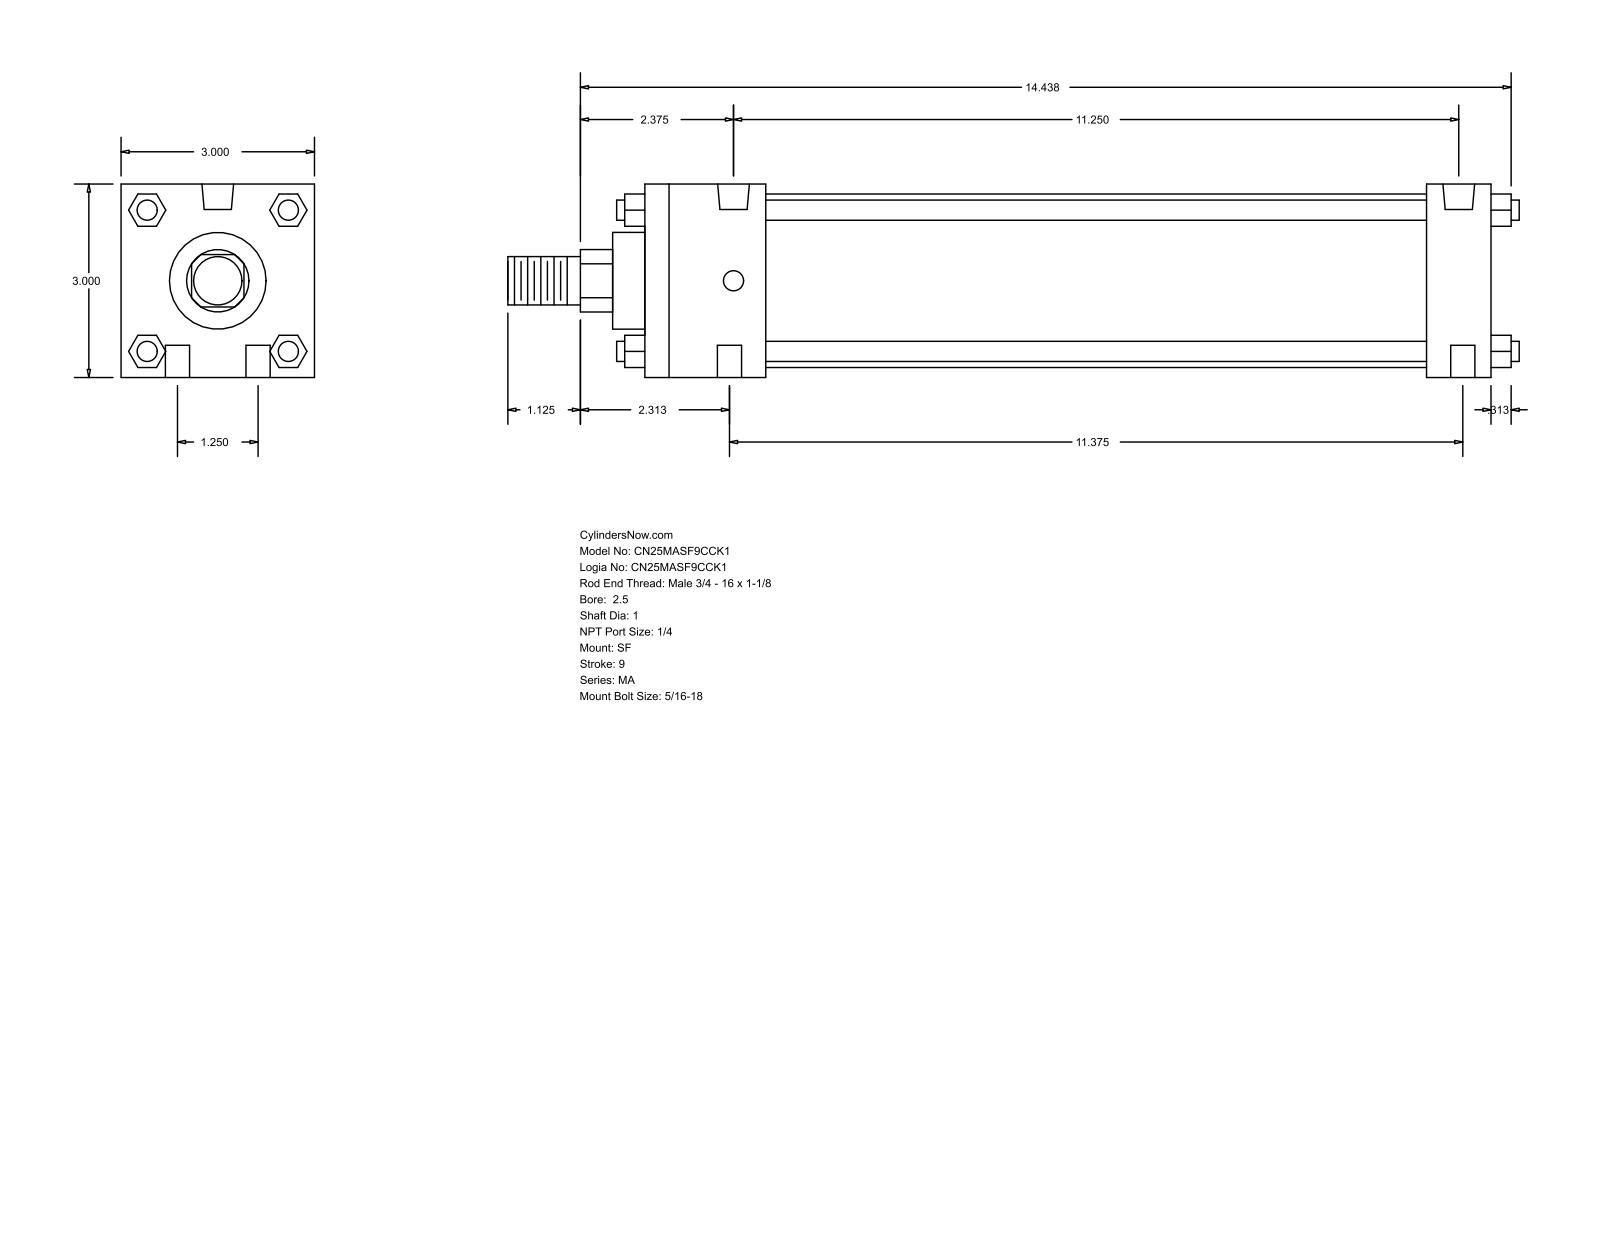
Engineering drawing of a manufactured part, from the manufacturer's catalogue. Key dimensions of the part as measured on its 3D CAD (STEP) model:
Part name (STEP PRODUCT): MA_SF__0250_1
STEP written by: GSSL Pune (CONFIG_CONTROL_DESIGN)
Units: millimetres
Bodies: 0 solids, 124 faces (94 planar, 30 cylindrical, 0 other)
Overall size (bounding box): 398.46 × 76.2 × 76.2
Round holes (diameter × count): ⌀9.53 ×4, ⌀7.94 ×2, ⌀12.49 ×2
Round bosses / shafts (diameter × count): ⌀7.94 ×4, ⌀68.33 ×1, ⌀38.1 ×1, ⌀25.4 ×1, ⌀19.05 ×1
Partial cylindrical surfaces — rounded edges, fillets, slot ends (radius × count): R12.29 ×1
Main face-to-face distances: 76.2, 333.37, 12.7, 307.98, 25.39, 47.63, 260.35, 285.74, 27.81, 48.17
Hole centre spacings: 15.96, 287.77, 31.76, 285.74, 288.92, 290.66
